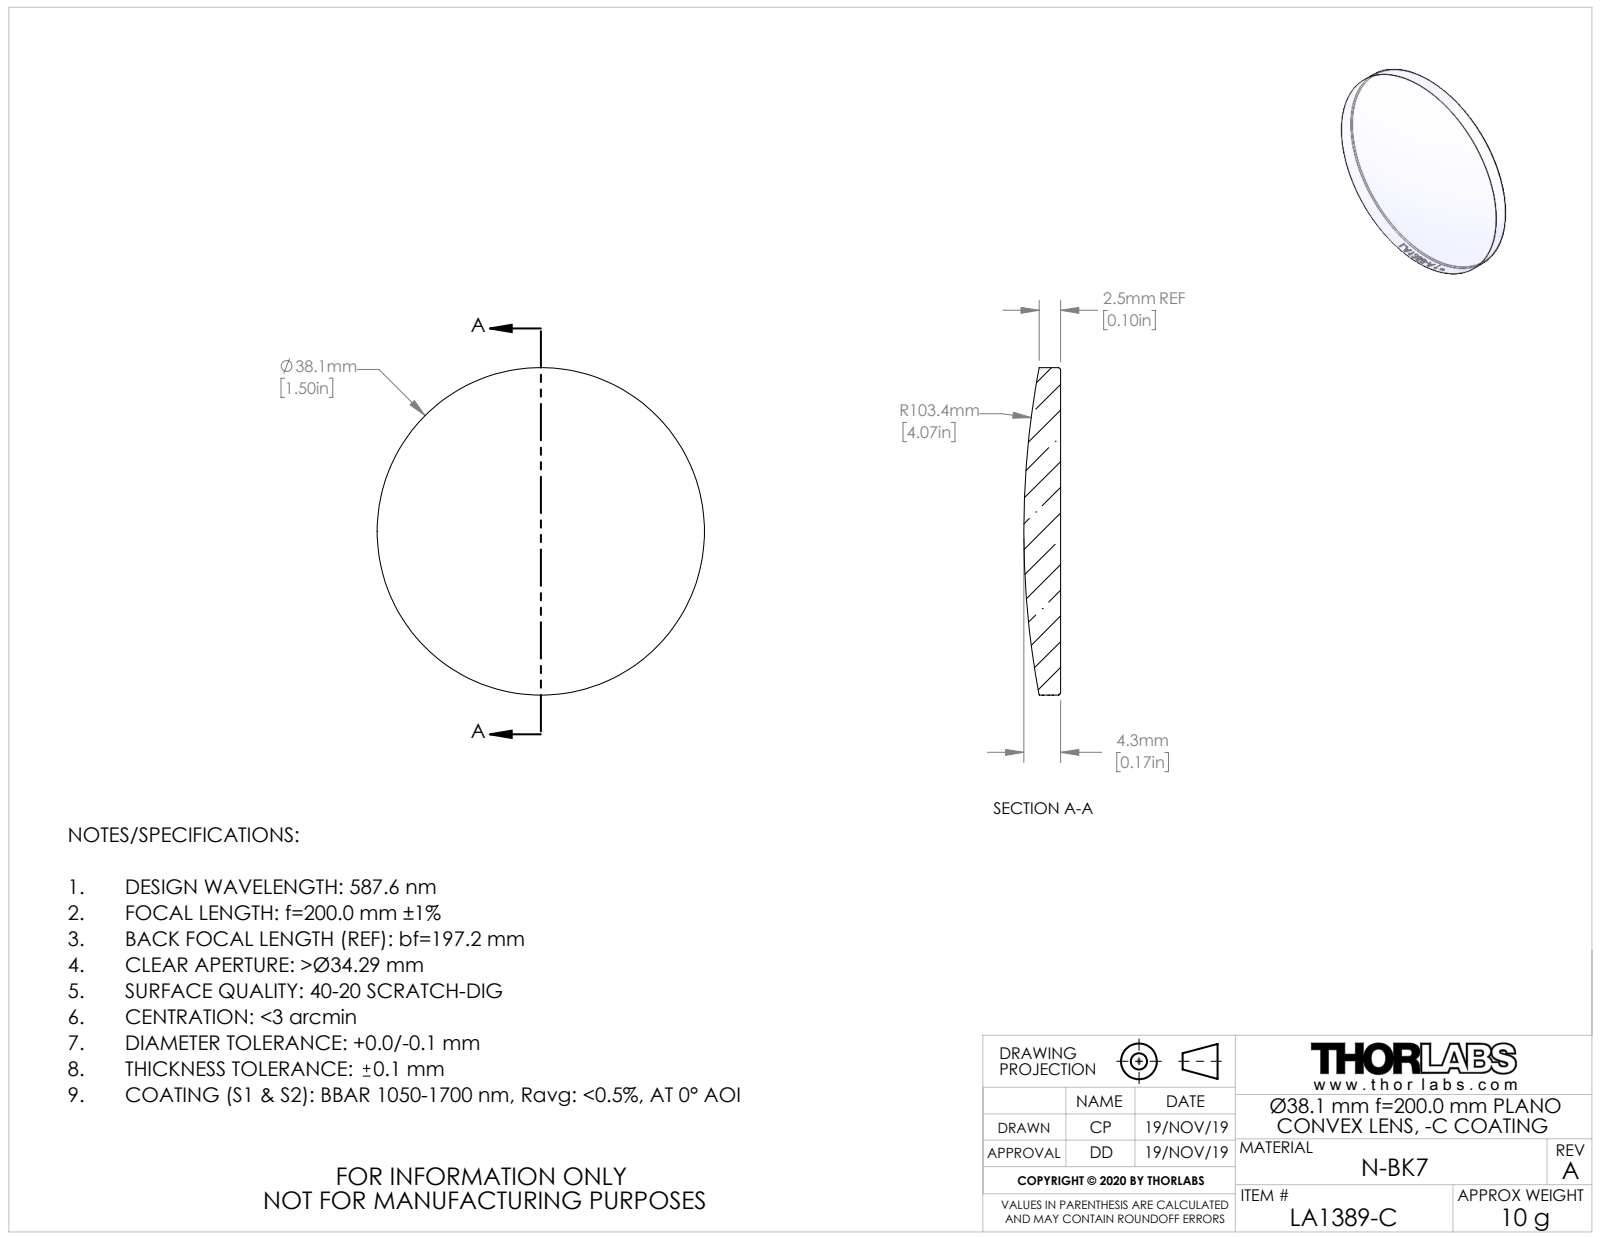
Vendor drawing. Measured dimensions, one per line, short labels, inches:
name: TTN200743-E0W
written by: SolidWorks 2018 (CONFIG_CONTROL_DESIGN)
unit: in
bodies: 1 solid, 24 faces (1 planar, 19 cylindrical, 4 other)
size: 1.5 × 1.5 × 0.168
volume: 0.235 in³; area: 3.991 in²
bosses: 1× ⌀1.5
